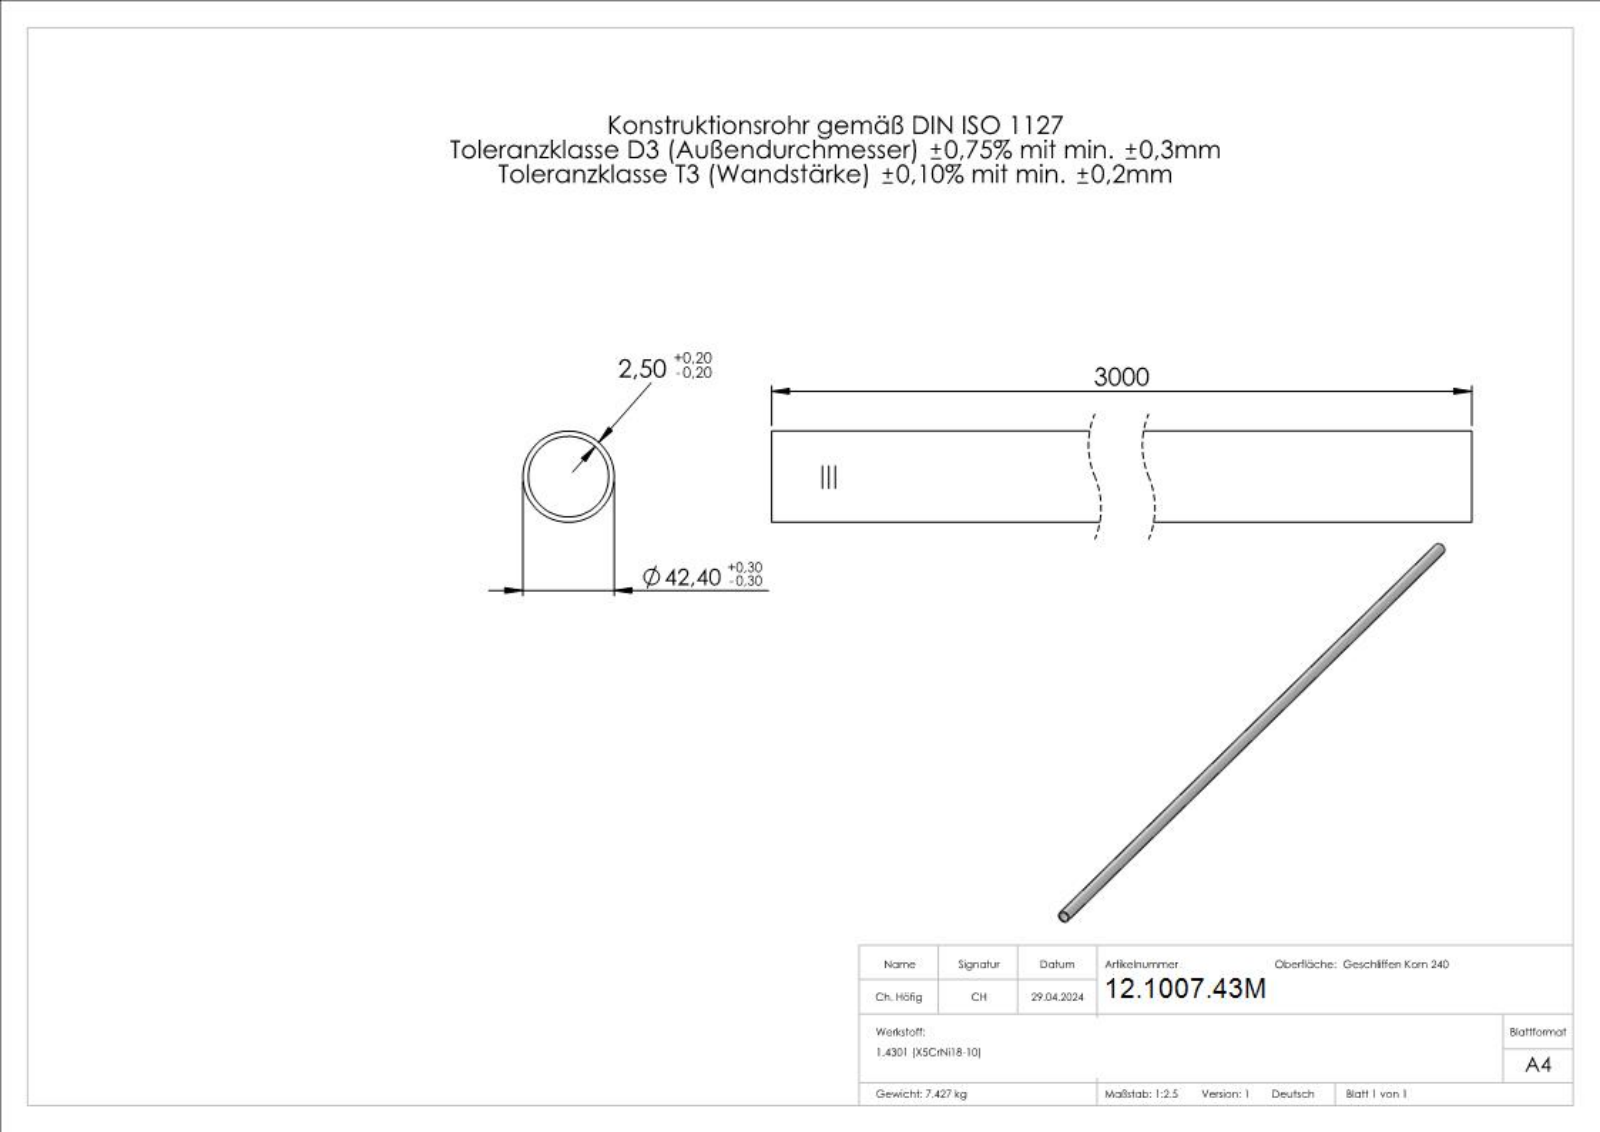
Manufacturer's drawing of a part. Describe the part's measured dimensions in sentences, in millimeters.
The part is named "55140-2403M". Its 3-D file was written by "SolidWorks 2018 (CONFIG_CONTROL_DESIGN)". It is 1 solid with 299 faces: 148 planar, 29 cylindrical and 122 other. Overall it measures 3000 by 42.4 by 42.4 millimeters. Its volume is 940 121 cubic millimeters and its surface area 752 732 square millimeters. Round holes: 1 of diameter 37.4. Round bosses or shafts: 1 of diameter 42.4. Partial cylindrical surfaces (rounded edges, fillets, slot ends): 1 of radius 18.8. The main face-to-face distances are 3000, 1.57, 0.79, 2.41, 0.73, 1.6, 0.53, 2.24, 2.53, 2.45.
